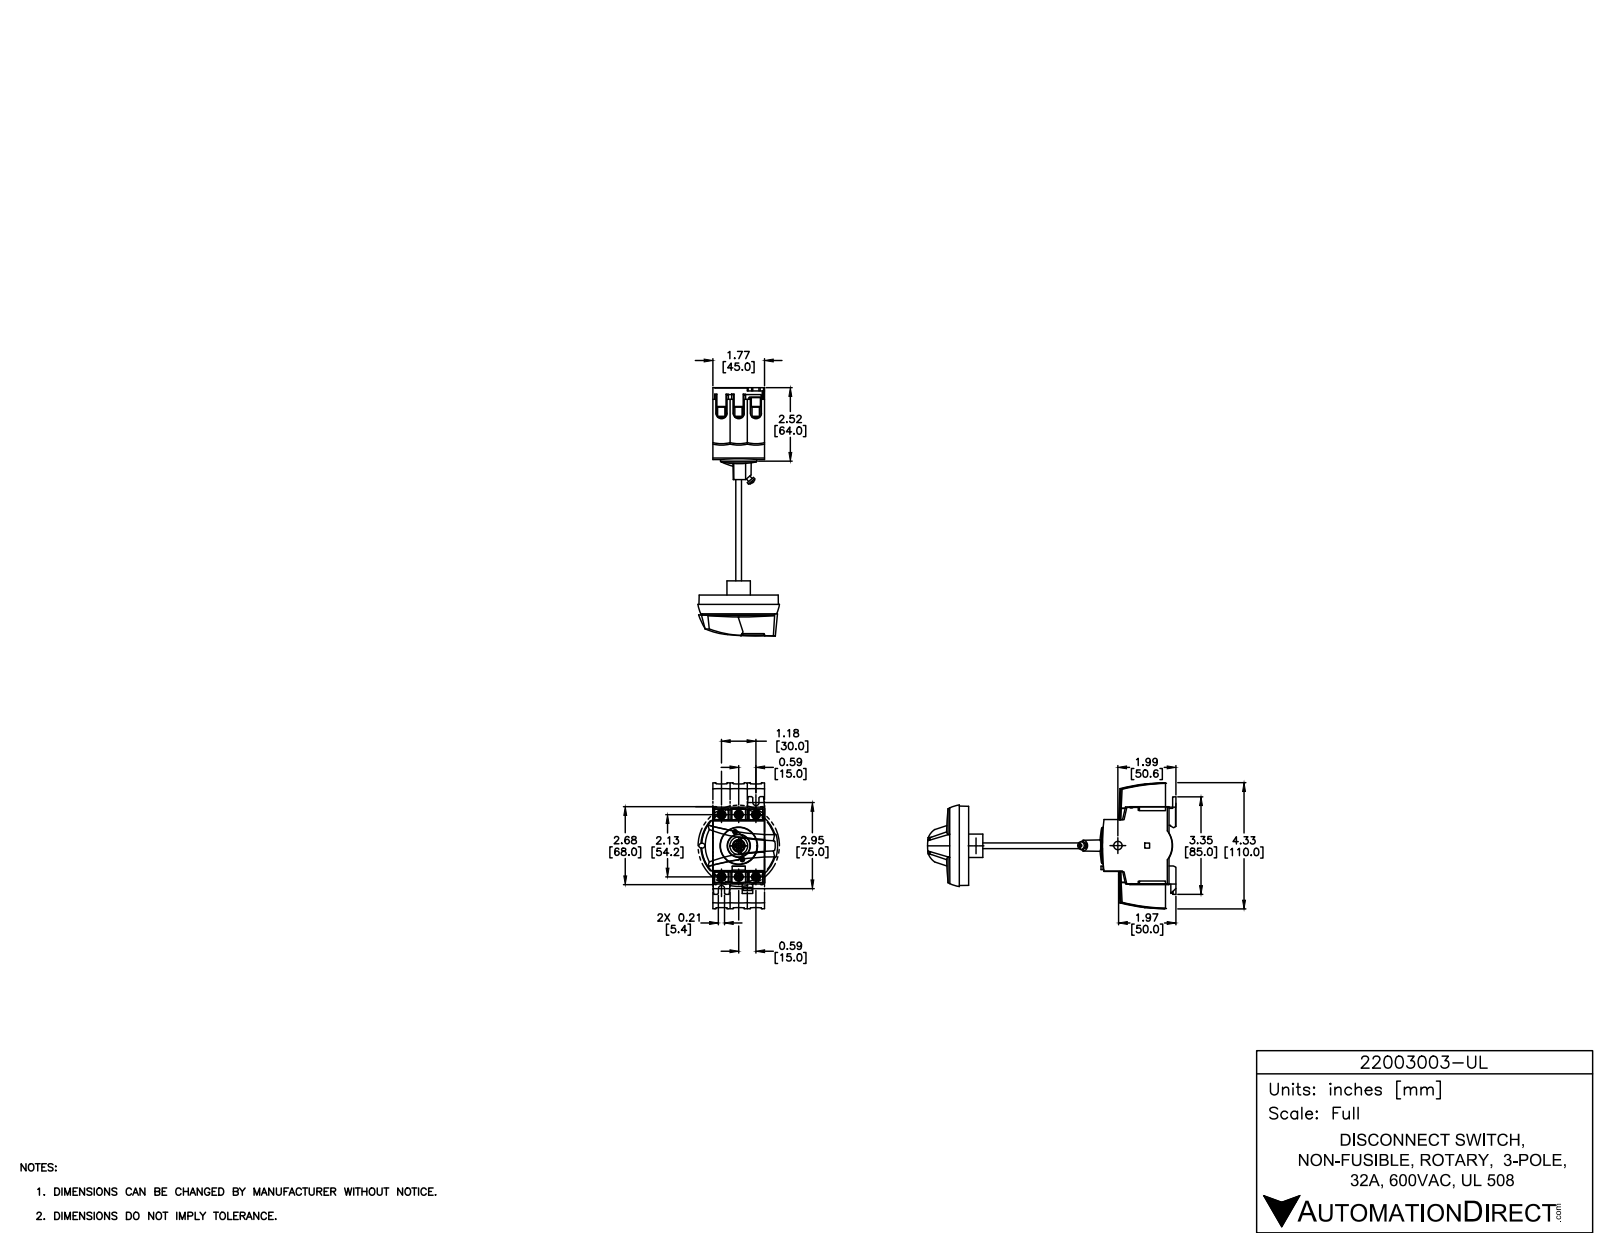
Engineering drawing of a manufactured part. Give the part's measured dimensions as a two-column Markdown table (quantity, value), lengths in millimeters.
| quantity | value |
| --- | --- |
| part name | 22003003-UL |
| STEP written by | SolidWorks 2015 (AUTOMOTIVE_DESIGN) |
| units | millimeters |
| bodies | 1 solid, 463 faces (389 planar, 50 cylindrical, 24 other) |
| overall size | 85 × 65.3 × 45 |
| volume | 155 600 mm³ |
| surface area | 25 950 mm² |
| round holes (diameter × count) | 6.6 × 6, 7.2 × 1, 31.6 × 1 |
| partial cylindrical surfaces (radius × count) | 0.3 × 13, 0.5 × 5, 4.2 × 4, 1 × 3, 2.7 × 2, 3.3 × 1, 9 × 1, 9.4 × 1 |
| main face-to-face distances | 45, 11, 56, 54.8, 67, 57.9, 15, 65.8, 1.2, 9.8 |
| hole center spacings | 15, 31, 56.2, 54.2, 27.1, 30, 62 |
